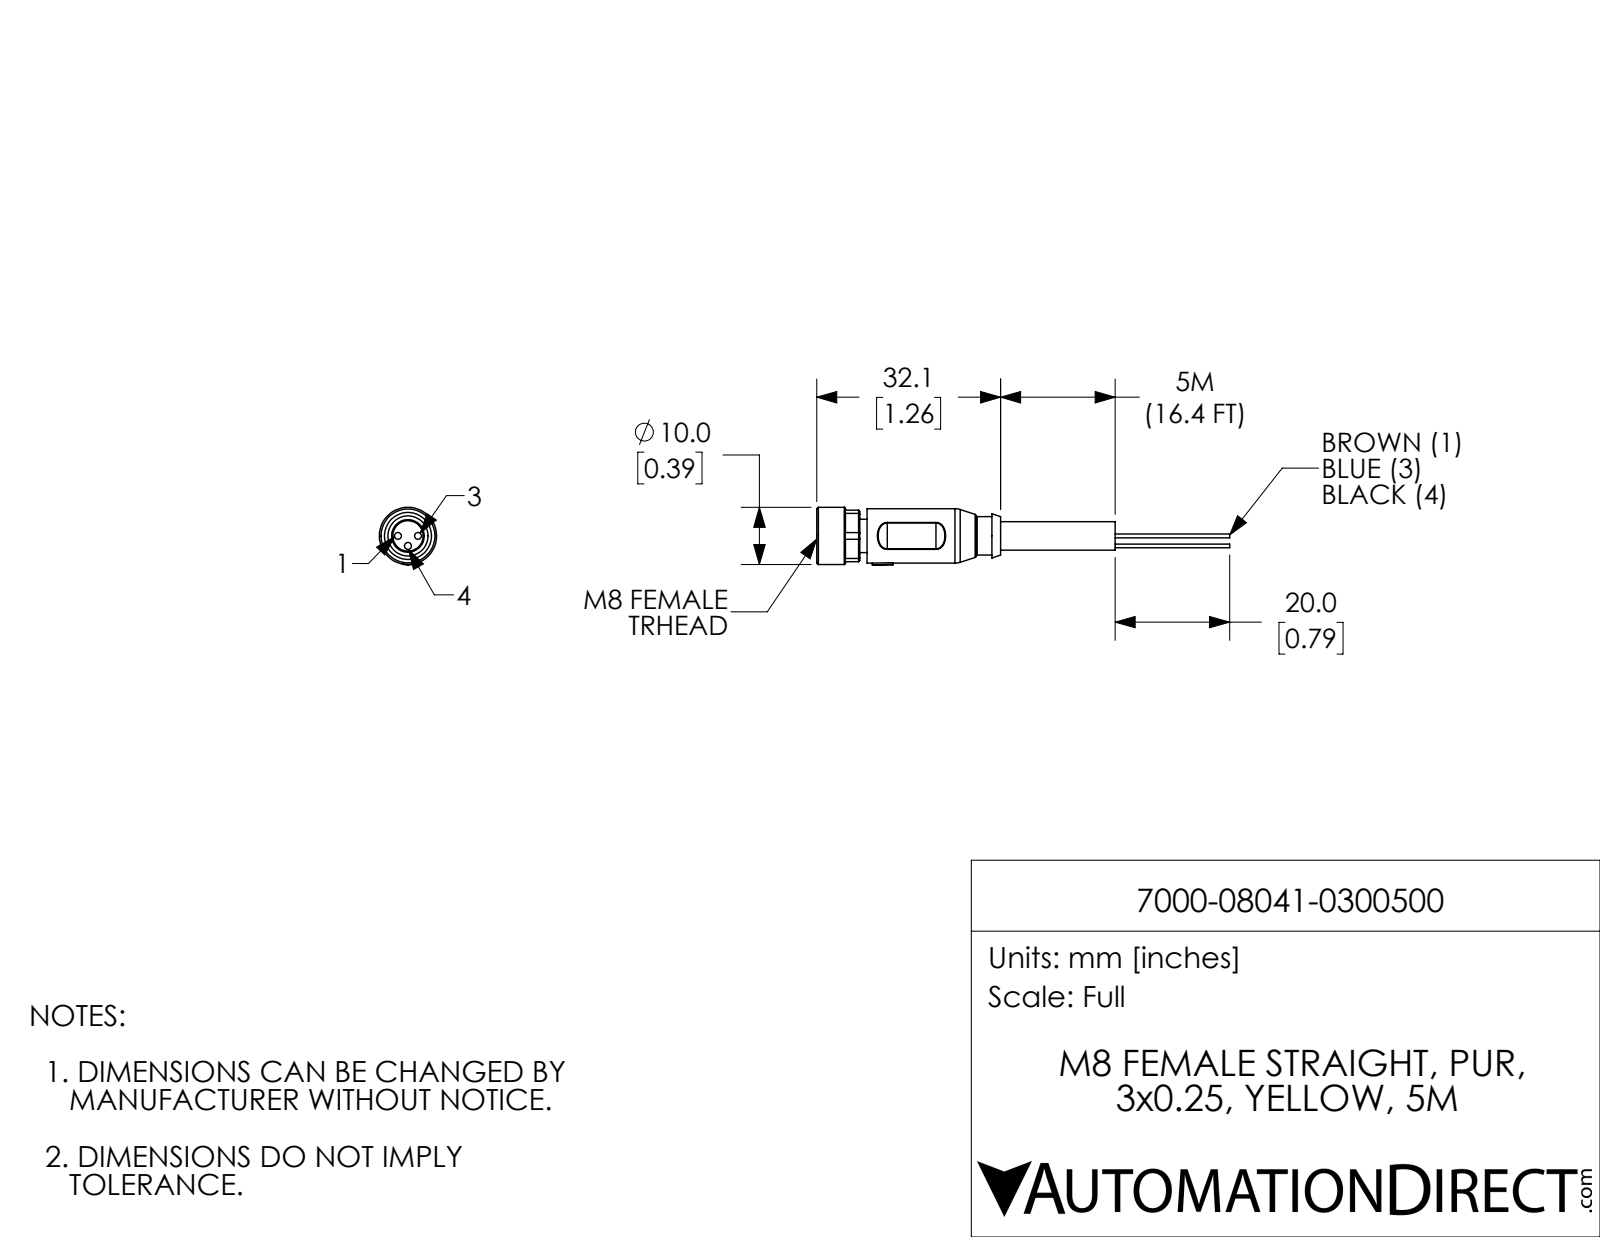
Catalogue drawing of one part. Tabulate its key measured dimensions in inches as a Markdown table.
| quantity | value |
| --- | --- |
| part name | 7000-08041-0300500 |
| STEP written by | SolidWorks 2021 (CONFIG_CONTROL_DESIGN) |
| units | inches |
| bodies | 1 solid, 109 faces (36 planar, 42 cylindrical, 31 other) |
| overall size | 2.839 × 0.396 × 0.394 |
| volume | 0.141 in³ |
| surface area | 2.851 in² |
| round holes (diameter × count) | 0.047 × 3, 0.276 × 1 |
| round bosses / shafts (diameter × count) | 0.026 × 3, 0.394 × 1, 0.374 × 1, 0.264 × 1, 0.228 × 1, 0.224 × 1, 0.197 × 1 |
| partial cylindrical surfaces (radius × count) | 0.008 × 4, 0.098 × 4, 0.193 × 1, 0.199 × 1 |
| main face-to-face distances | 0.327, 0.051, 0.969, 0.354, 0.059, 0.028, 0.268, 0.319, 2.024, 1.756 |
| hole center spacings | 0.069, 0.097, 0.138 |
